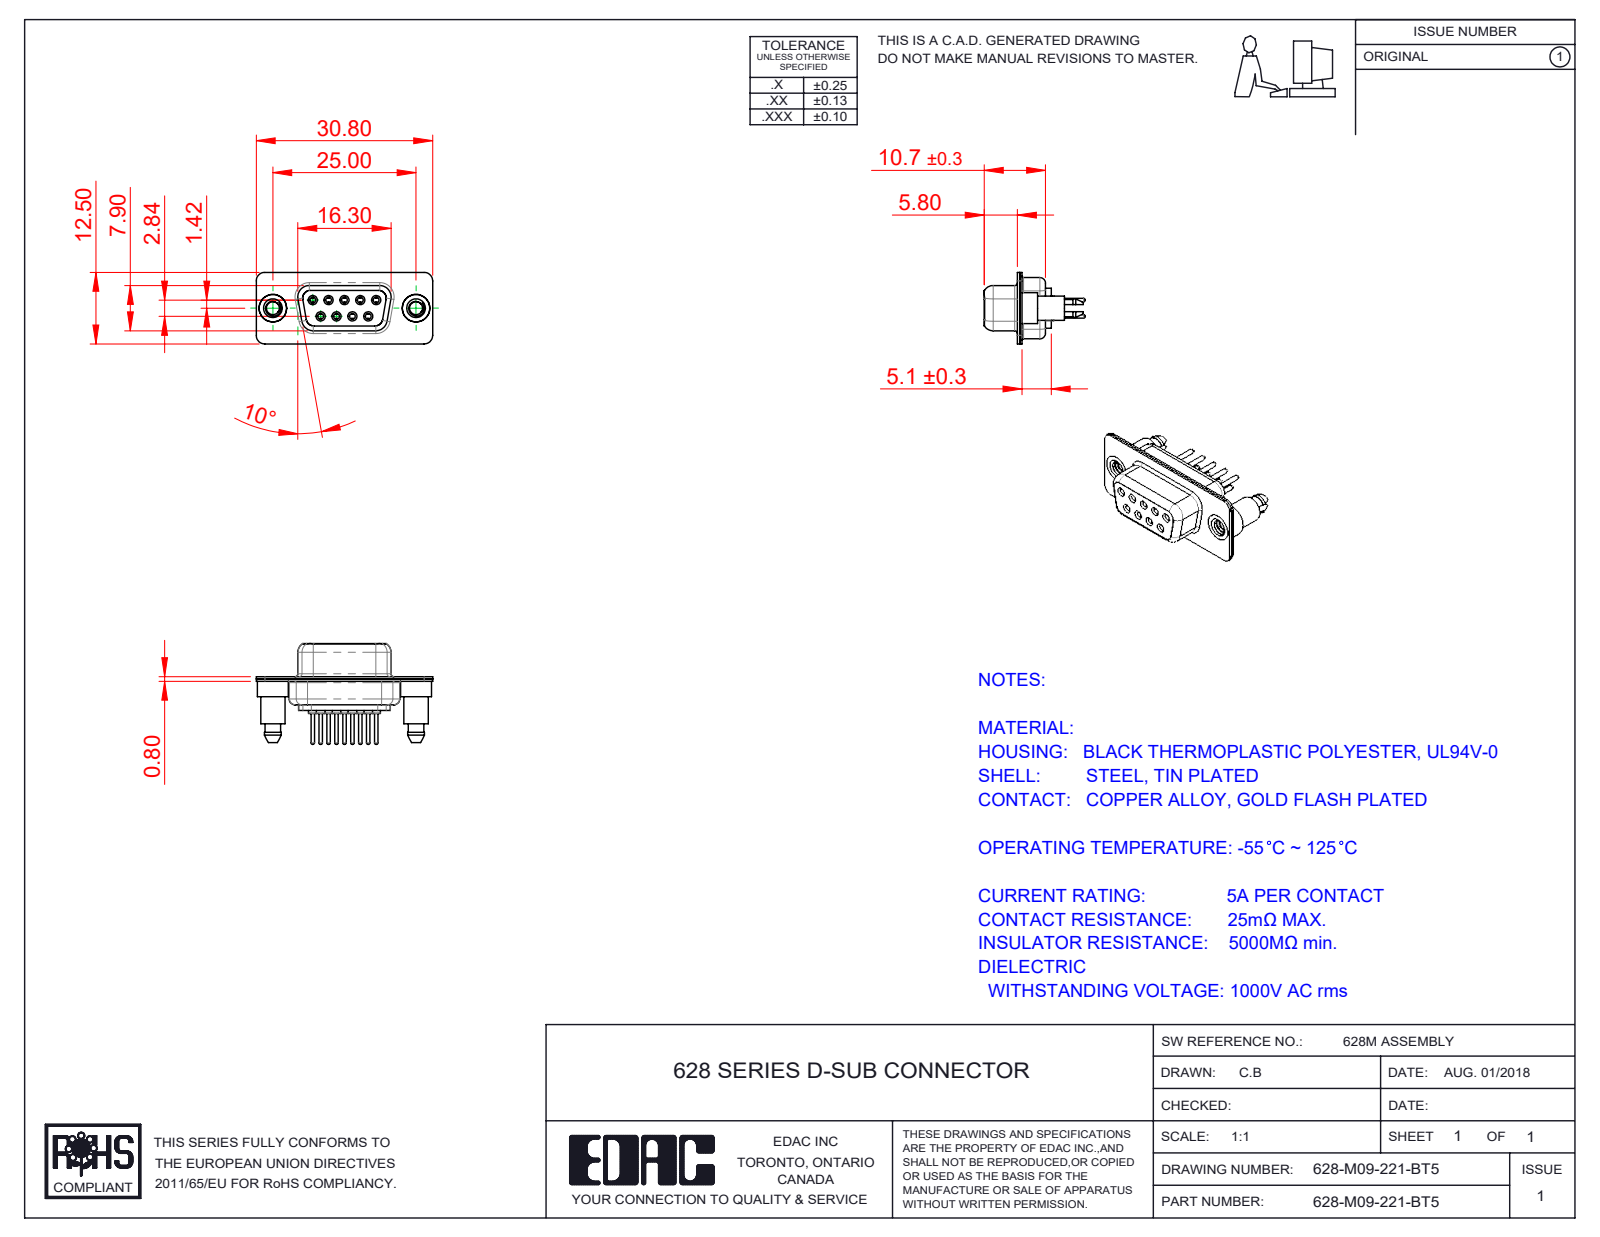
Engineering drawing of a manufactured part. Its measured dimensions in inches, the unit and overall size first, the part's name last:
Units: inches
Overall size (bounding box): 1.213 × 0.693 × 0.492
Round holes (diameter × count): ⌀0.039 ×9, ⌀0.043 ×9, ⌀0.067 ×9, ⌀0.071 ×9, ⌀0.079 ×9, ⌀0.089 ×2, ⌀0.157 ×2, ⌀0.189 ×2
Round bosses / shafts (diameter × count): ⌀0.087 ×9, ⌀0.063 ×9, ⌀0.059 ×9, ⌀0.024 ×9, ⌀0.213 ×2, ⌀0.193 ×2, ⌀0.167 ×2
Partial cylindrical surfaces — rounded edges, fillets, slot ends (radius × count): R0.059 ×18, R0.079 ×12, R0.063 ×10, R0.053 ×8, R0.01 ×4, R0.02 ×4, R0.024 ×4, R0.026 ×4
Main face-to-face distances: 0.016, 0.055, 0.018, 0.333, 0.031, 0.071, 0.039, 0.35, 0.244, 0.278
Hole centre spacings: 0.124, 0.109, 0.218, 0.198, 0.198, 0.327, 0.28, 0.294
Volume: 0.112 in³ · Surface area: 7.37 in²
Bodies: 14 solids, 824 faces (218 planar, 340 cylindrical, 266 other)
Part name (STEP PRODUCT): 628M Housing_09 Contacts; 628M Contact Row 2_21; 628M Shell Front_09 Contacts; 628M Shell Rear_09 Contacts (+3 more)
STEP written by: SolidWorks 2020 (CONFIG_CONTROL_DESIGN)
